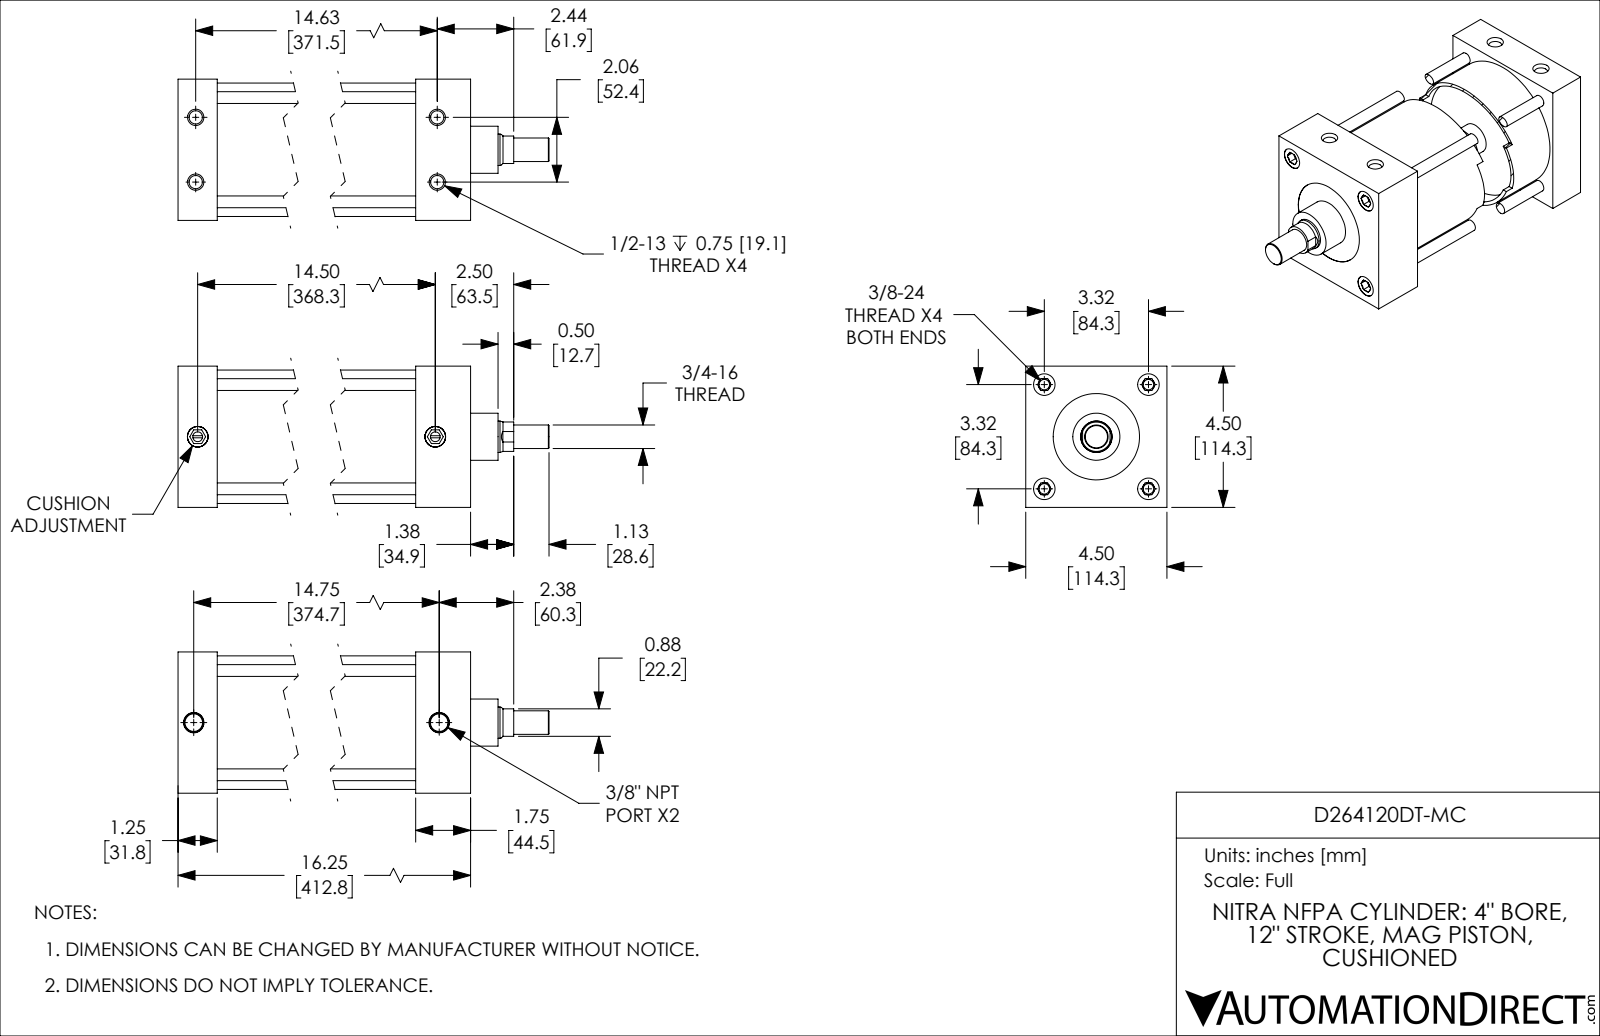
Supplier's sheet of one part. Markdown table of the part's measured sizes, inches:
| quantity | value |
| --- | --- |
| part name | D264120DT-MC_PISTON_KK1; D264120DT-MC; D264120DT-MC_CUSHION; D264120DT-MC_BODY |
| STEP written by | SolidWorks 2019 (CONFIG_CONTROL_DESIGN) |
| units | inches |
| bodies | 4 solids, 246 faces (90 planar, 78 cylindrical, 78 other) |
| overall size | 18.75 × 4.5 × 4.5 |
| volume | 113.1 in³ |
| surface area | 662 in² |
| round holes (diameter × count) | 0.332 × 4, 0.422 × 4, 0.687 × 4, 0.312 × 2, 0.562 × 2, 0.656 × 2, 1.001 × 1, 2.75 × 1, 4.001 × 1 |
| round bosses / shafts (diameter × count) | 0.375 × 4, 0.657 × 2, 4.251 × 1, 3.999 × 1, 1.5 × 1, 0.999 × 1, 0.75 × 1 |
| partial cylindrical surfaces (radius × count) | 0.469 × 1 |
| main face-to-face distances | 1.25, 4.5, 14.5, 13.25, 16.25, 15, 1.75, 2.5, 12, 13.75 |
| hole center spacings | 1.033, 2.347, 3.32, 14.724, 2.062, 4.695, 14.625, 14.769 |
